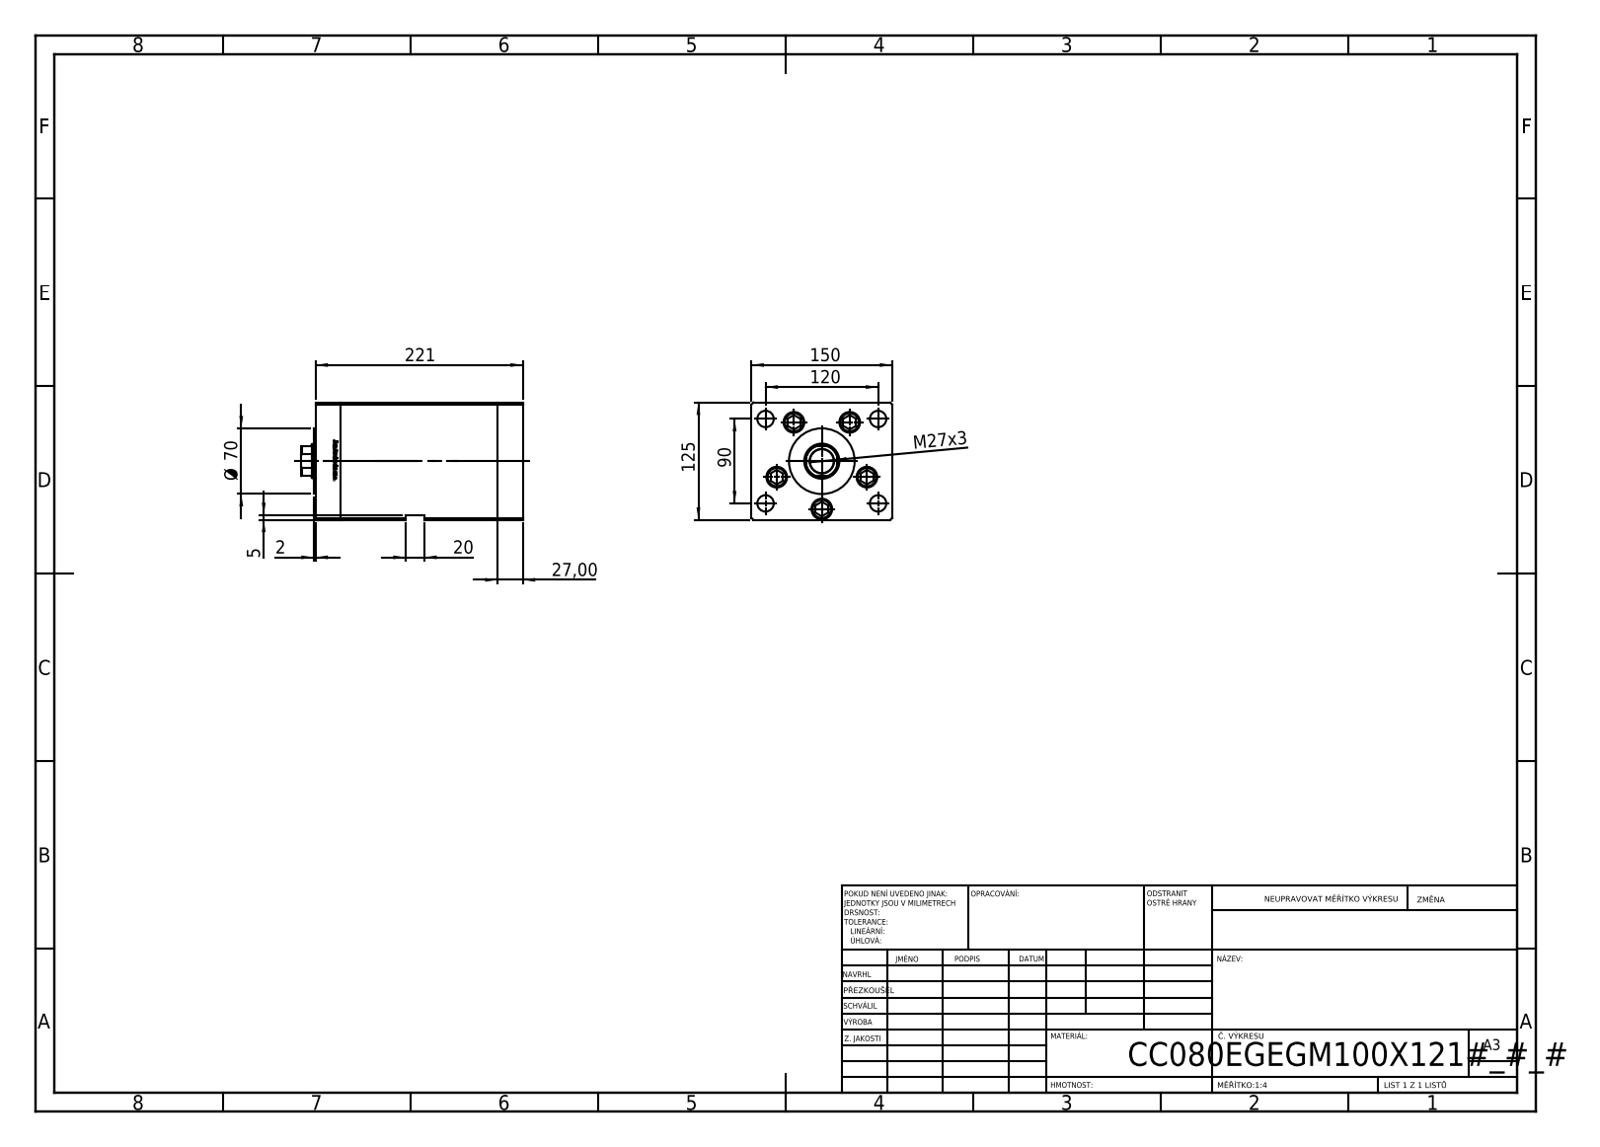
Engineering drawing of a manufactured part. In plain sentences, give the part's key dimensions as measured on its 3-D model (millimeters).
The part is named "V220C_FRONT_E; V220C_E MIDDLE; V220C_VC_E; V220C BACK_E (+1 more)". Its 3-D file was written by "SolidWorks 2019 (CONFIG_CONTROL_DESIGN)". It is 14 solids with 1214 faces: 475 planar, 165 cylindrical and 574 other. Overall it measures 236 by 150 by 125 millimeters. Its volume is 3 421 000 cubic millimeters and its surface area 396 942 square millimeters. Round holes: 9 of diameter 17.5, 5 of diameter 22, 4 of diameter 17, 4 of diameter 23, 2 of diameter 2, 2 of diameter 13.16, 1 of diameter 25.5, 1 of diameter 36, 1 of diameter 37.5. Round bosses or shafts: 5 of diameter 21, 5 of diameter 8, 1 of diameter 80, 1 of diameter 70. Partial cylindrical surfaces (rounded edges, fillets, slot ends): 2 of radius 0.93, 1 of radius 17.5. The main face-to-face distances are 27, 194, 167, 125, 150, 33.5, 6.5, 221, 160.5, 187.5. The hole center spacings are 51, 75, 30.43, 30.48, 58.89, 60.3, 61.25, 63.14.
